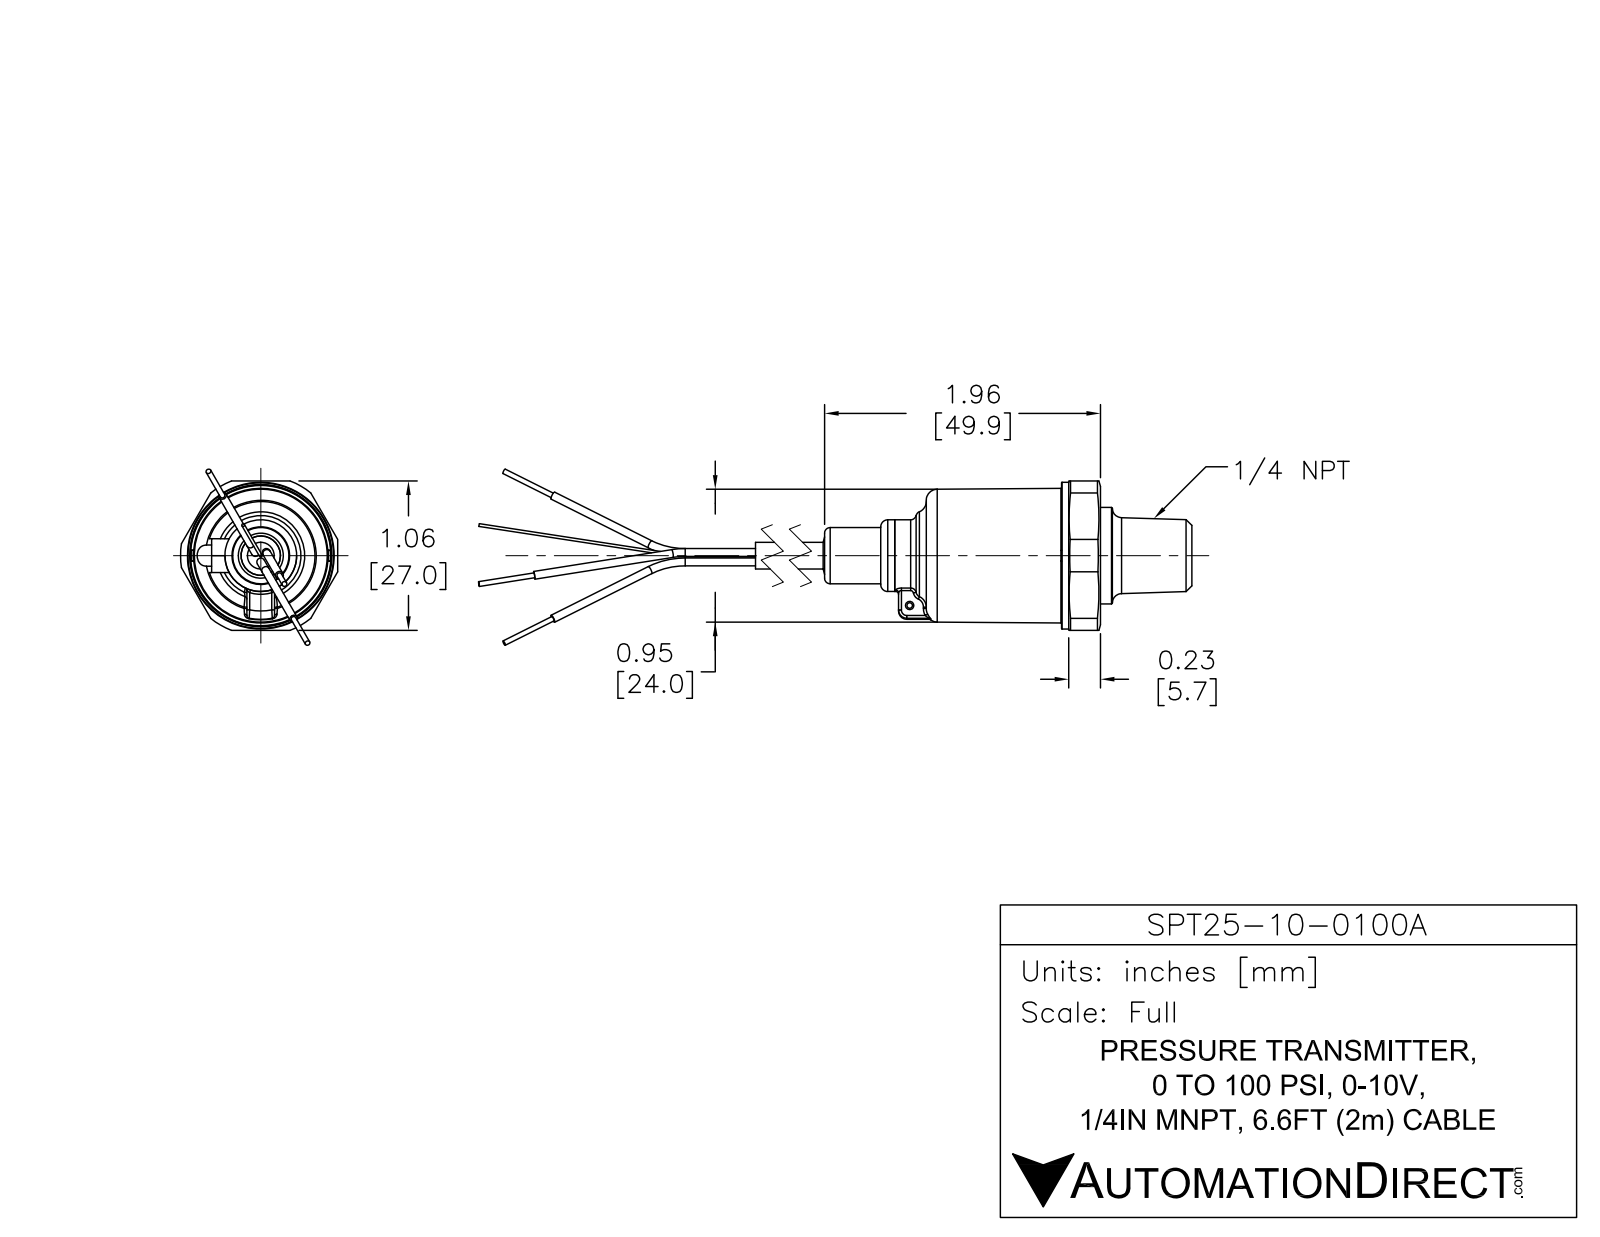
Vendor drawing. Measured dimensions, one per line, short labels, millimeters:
name: SPT25-10-0100A
written by: SolidWorks 2017 (AUTOMOTIVE_DESIGN)
unit: mm
bodies: 7 solids, 116 faces (32 planar, 49 cylindrical, 35 other)
size: 153.3 × 29 × 27.09
volume: 20 801 mm³; area: 7 170 mm²
holes: 1× ⌀1, 1× ⌀3.3
bosses: 6× ⌀1.4, 5× ⌀0.75, 1× ⌀26.75, 1× ⌀24, 1× ⌀17.5, 1× ⌀14, 1× ⌀13, 1× ⌀10
rounds: 1× R2, 1× R14.5
face distances: 6.75, 24, 17.25, 42.75, 49.5, 66.75, 44, 1.25, 5.5, 22.75
